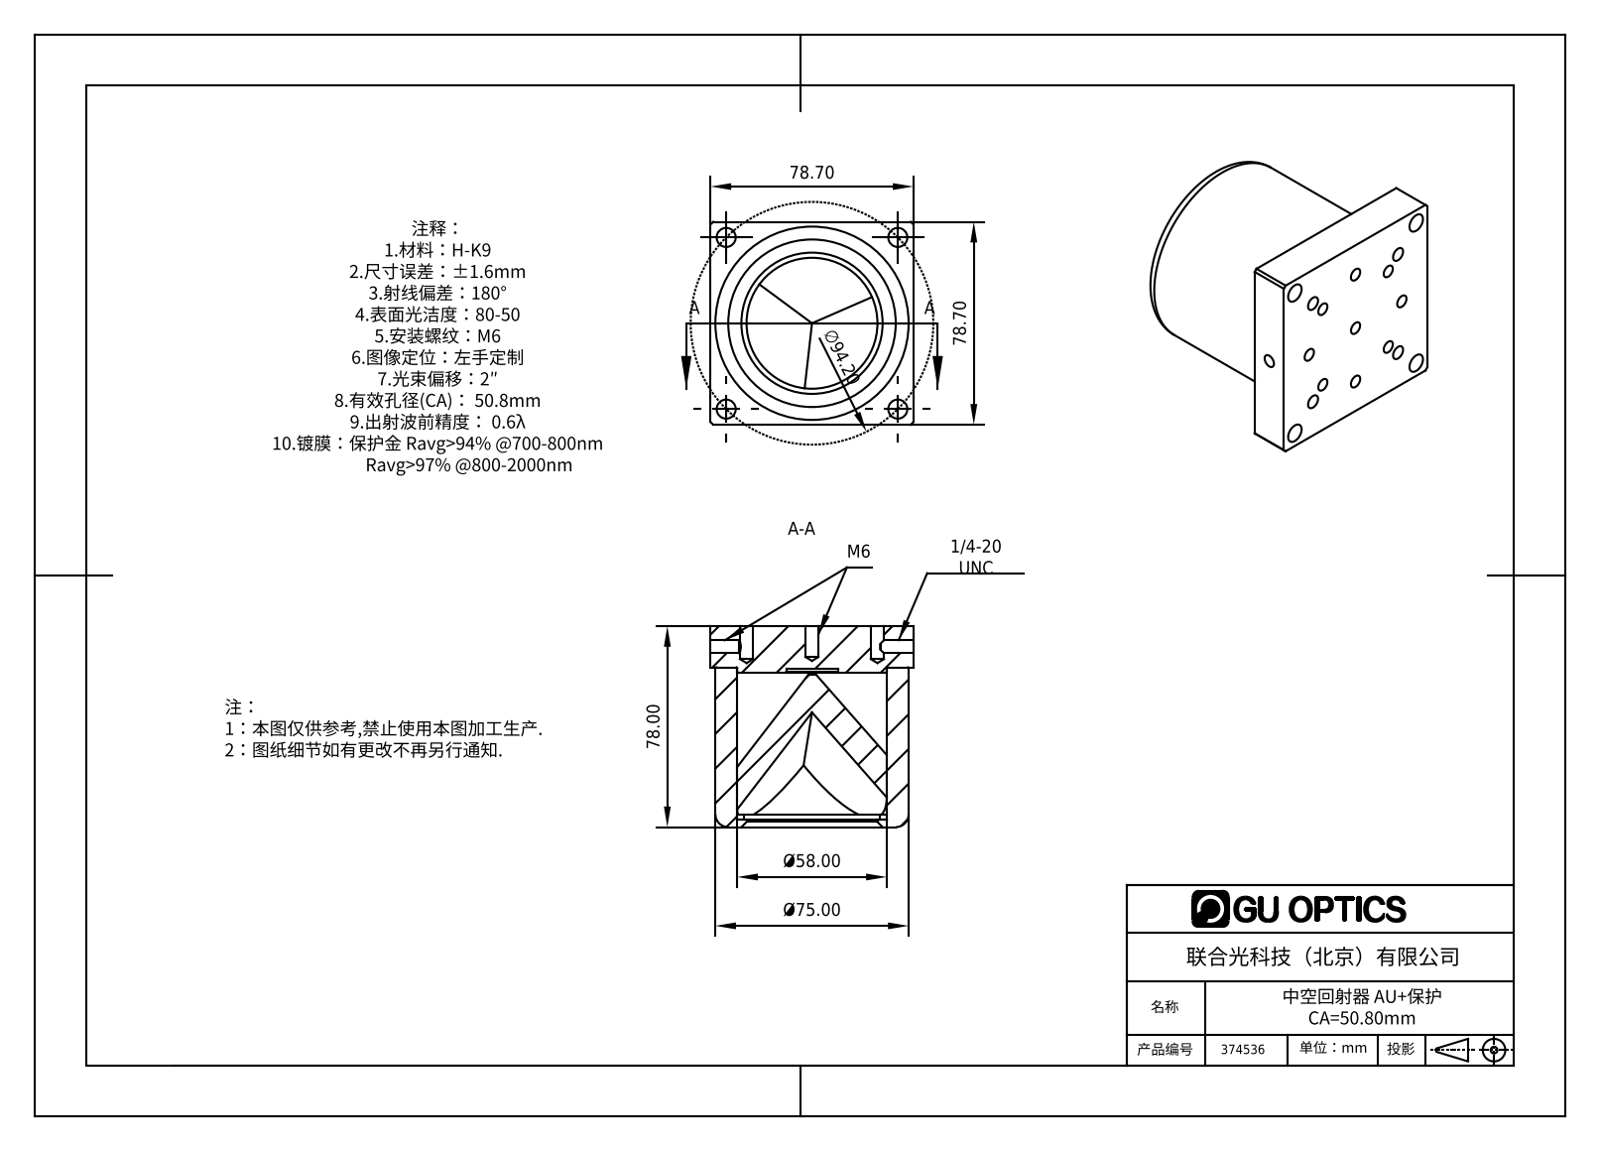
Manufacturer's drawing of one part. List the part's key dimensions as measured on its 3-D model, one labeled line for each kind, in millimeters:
Part name (STEP PRODUCT): 374530
STEP written by: SolidWorks 2016 (AUTOMOTIVE_DESIGN)
Units: millimetres
Bodies: 8 solids, 251 faces (91 planar, 86 cylindrical, 74 other)
Overall size (bounding box): 78.7 × 78.7 × 78
Volume: 252 195 mm³ · Surface area: 66 504 mm²
Round holes (diameter × count): ⌀5 ×6, ⌀5.11 ×5, ⌀2.5 ×4, ⌀3.5 ×4, ⌀5.5 ×4, ⌀7.4 ×4, ⌀20 ×1, ⌀50.8 ×1, ⌀53 ×1
Round bosses / shafts (diameter × count): ⌀3 ×4, ⌀75 ×1, ⌀58 ×1
Main face-to-face distances: 16, 9.5, 2, 78.7, 18, 57, 9.49, 59, 75, 3
Hole centre spacings: 19.44, 23.42, 25.4, 34.22, 35.92, 41.64, 46.93, 53.51
